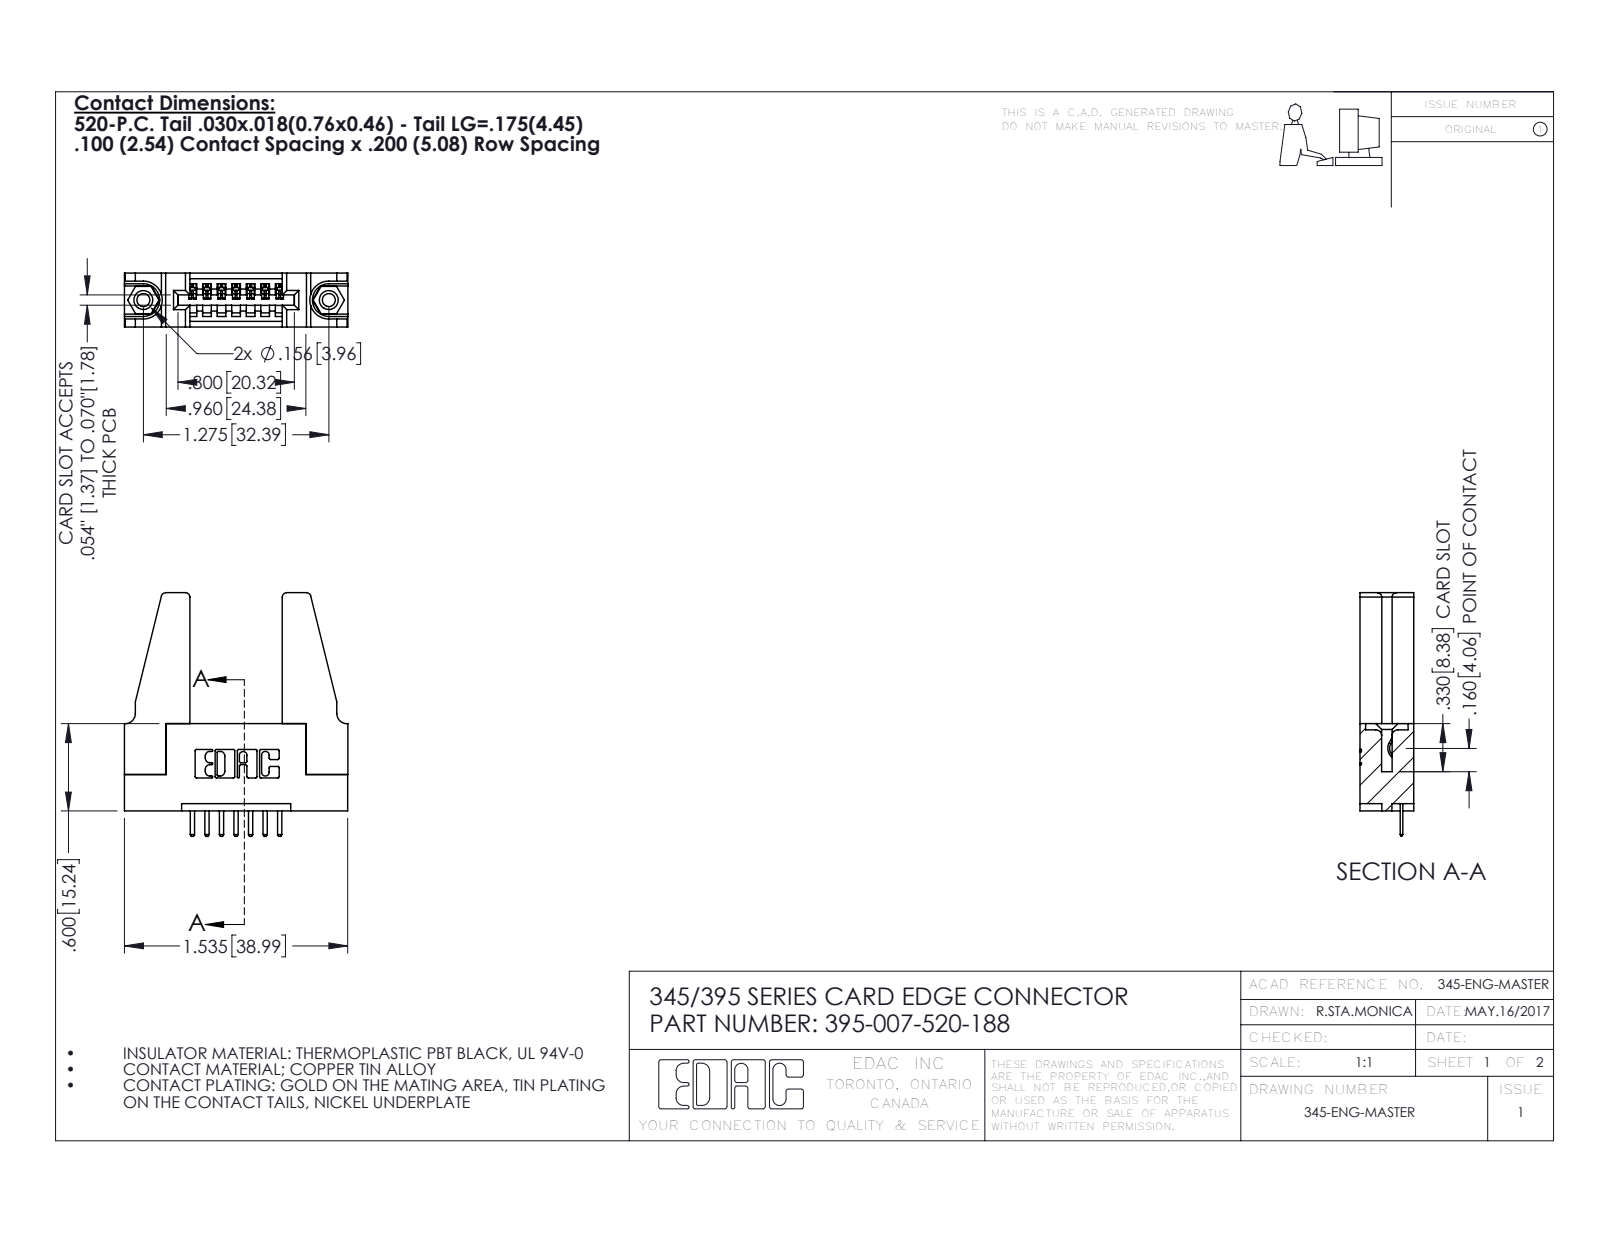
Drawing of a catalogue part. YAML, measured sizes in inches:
part_name: "345-292-001_345-293-120; 345-220-078_345-220-088; 345 Part_Flush Mounting Lugs - 0.156 Dia-TH; 345-250-001_345-250-001-102 (+1 more)"
step_written_by: "SolidWorks 2016 (CONFIG_CONTROL_DESIGN)"
units: inches
bodies: {solids: 12, faces: 684, planar: 446, cylindrical: 222, other: 16}
overall_size: [1.675, 1.536, 0.37]
volume: 0.406
surface_area: 11.01
round_holes:
  - {diameter: 0.089, count: 2}
  - {diameter: 0.125, count: 2}
  - {diameter: 0.156, count: 2}
  - {diameter: 0.064, count: 1}
round_bosses_or_shafts:
  - {diameter: 0.155, count: 2}
partial_cylinders:
  - {radius: 0.01, count: 22}
  - {radius: 0.01, count: 16}
  - {radius: 0.006, count: 14}
  - {radius: 0.03, count: 8}
  - {radius: 0.007, count: 6}
  - {radius: 0.031, count: 6}
  - {radius: 0.026, count: 3}
  - {radius: 0.031, count: 2}
face_to_face_distances: [0.37, 0.072, 0.298, 0.2, 0.148, 0.15, 0.25, 0.6, 0.35, 0.077]
hole_center_spacings: [0.27, 1.045, 1.275]
